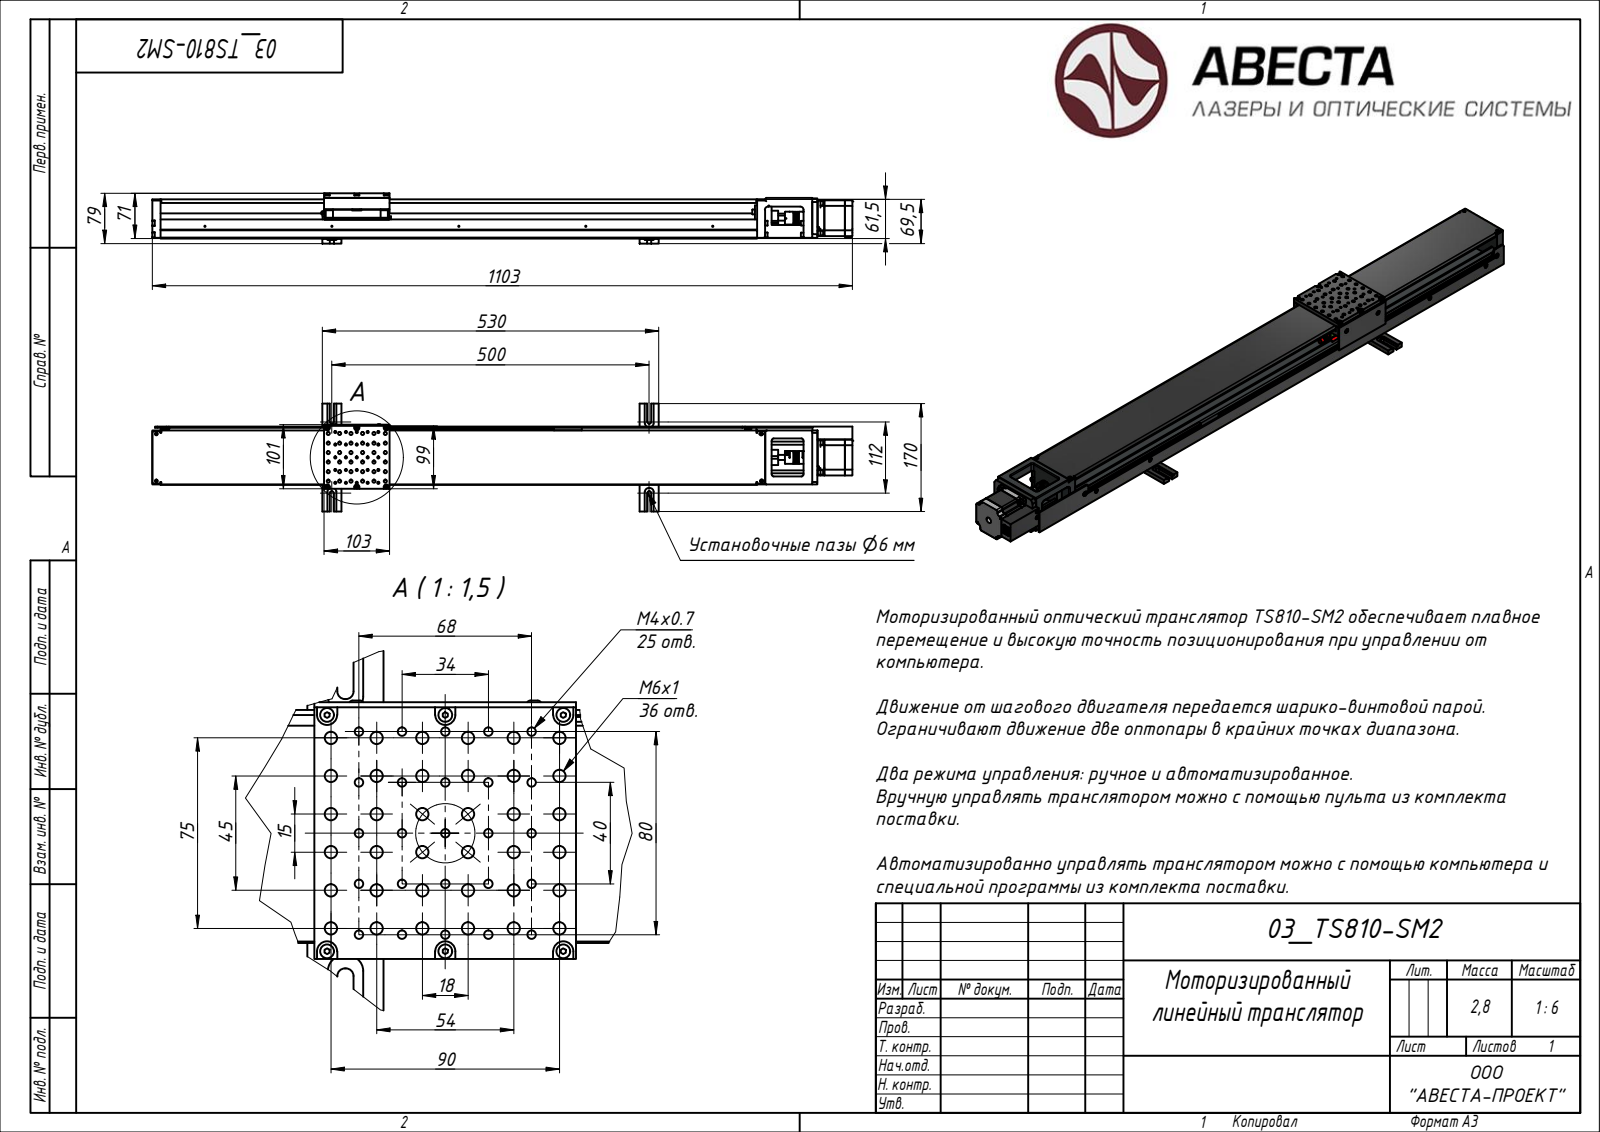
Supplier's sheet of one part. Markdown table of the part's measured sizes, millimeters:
| quantity | value |
| --- | --- |
| STEP written by | Rhino 7.34 (AUTOMOTIVE_DESIGN) |
| units | millimeters |
| bodies | 0 solids, 2567 faces (1016 planar, 902 cylindrical, 649 other) |
| overall size | 1103 × 170 × 79 |
| round holes (diameter × count) | 3.24 × 31, 11 × 22, 6.6 × 16, 4.92 × 14, 4.92 × 11, 2.02 × 4, 2.11 × 4, 3 × 4, 3.4 × 4, 5 × 4, 6.5 × 4, 7 × 4 |
| round bosses / shafts (diameter × count) | 7.5 × 10, 7 × 8, 5.5 × 8, 3 × 6, 10 × 4, 6 × 4, 4 × 4, 2 × 4 |
| partial cylindrical surfaces (radius × count) | 3 × 33, 1.5 × 25, 2.46 × 15, 2.46 × 15, 4 × 15, 2.5 × 12, 1 × 9, 0.5 × 8 |
| main face-to-face distances | 1.5, 0.5, 60, 2, 61.5, 1, 59.5, 61, 13, 85 |
| hole center spacings | 26.25, 39.45, 43.46, 17, 20, 52.5, 54.78, 62.36 |
